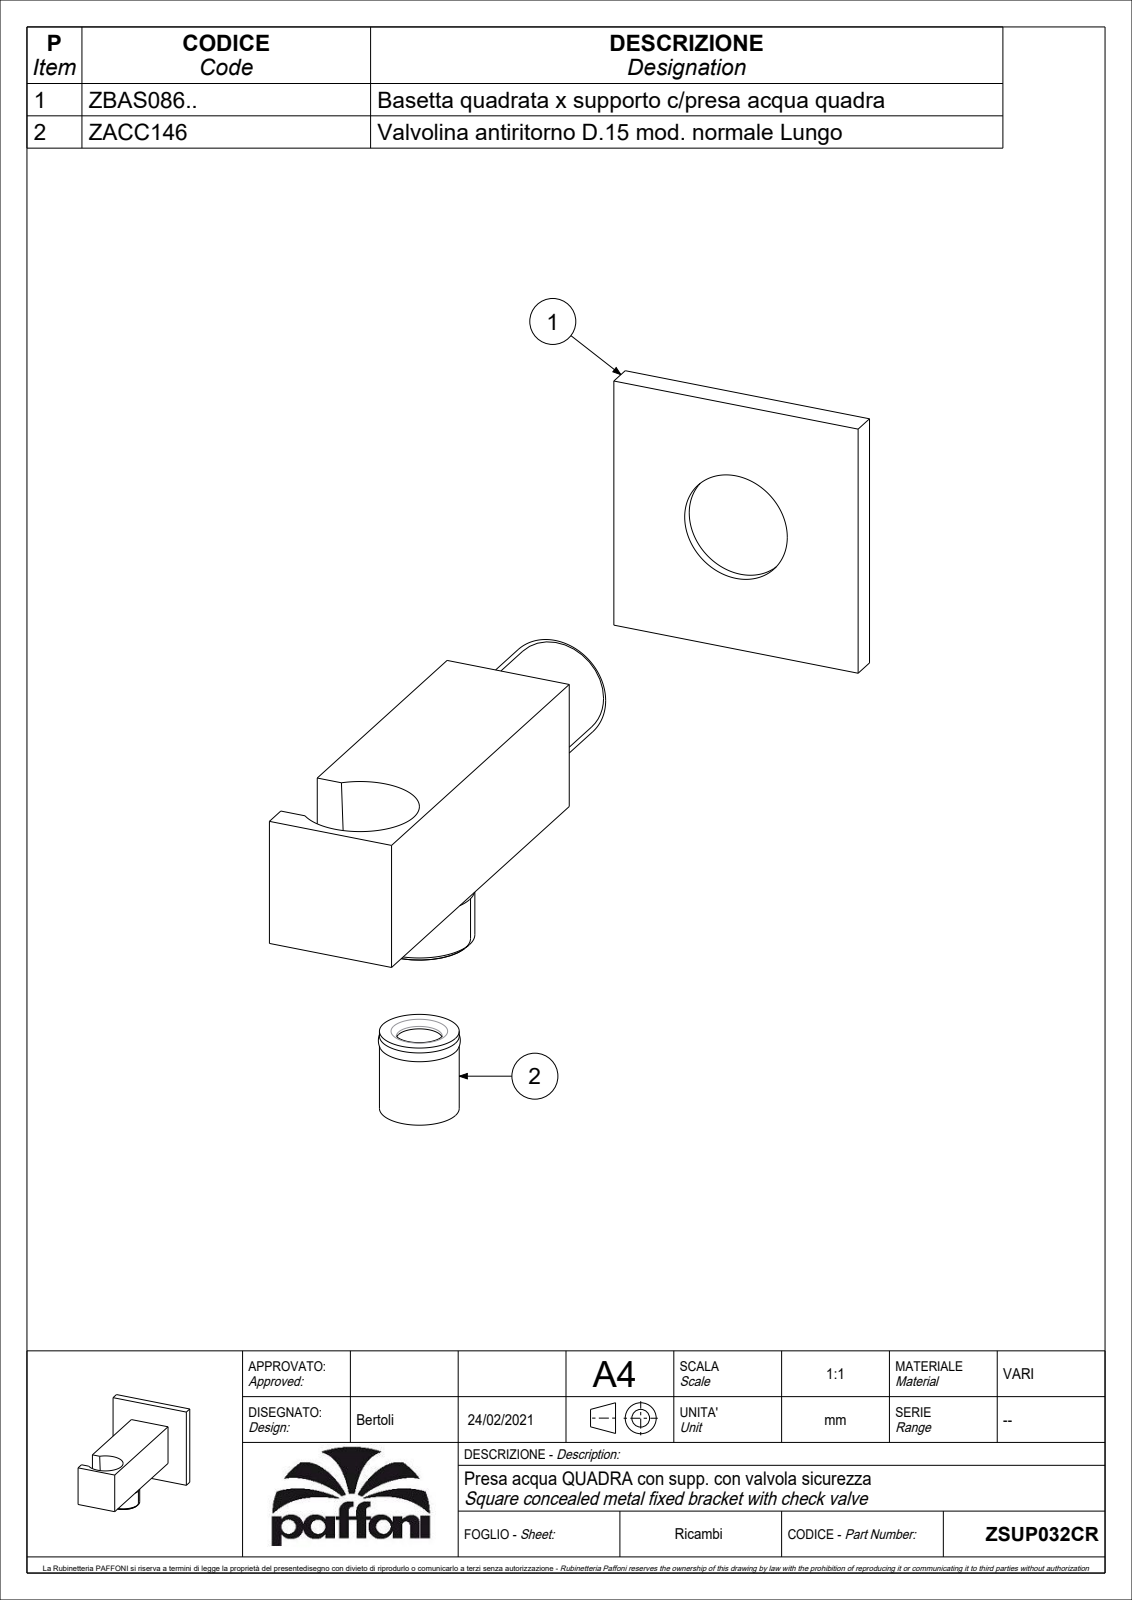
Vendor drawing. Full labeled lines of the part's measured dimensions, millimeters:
Part name (STEP PRODUCT): ZSUP032CR
STEP written by: CREO PARAMETRIC BY PTC INC, 2020044 (CONFIG_CONTROL_DESIGN)
Units: millimetres
Bodies: 2 solids, 163 faces (70 planar, 54 cylindrical, 39 other)
Overall size (bounding box): 83 × 50.5 × 50
Volume: 39 108 mm³ · Surface area: 23 918 mm²
Round holes (diameter × count): ⌀15 ×2, ⌀19 ×2, ⌀12 ×1, ⌀21 ×1, ⌀22.3 ×1, ⌀34 ×1, ⌀42 ×1
Round bosses / shafts (diameter × count): ⌀20.6 ×2, ⌀36 ×1, ⌀22 ×1, ⌀18.5 ×1, ⌀17 ×1, ⌀15.5 ×1
Partial cylindrical surfaces — rounded edges, fillets, slot ends (radius × count): R2.1 ×2, R2.5 ×2, R5.25 ×1
Main face-to-face distances: 25, 5, 12.5, 37.5, 2, 2.5, 78, 3, 50, 83
